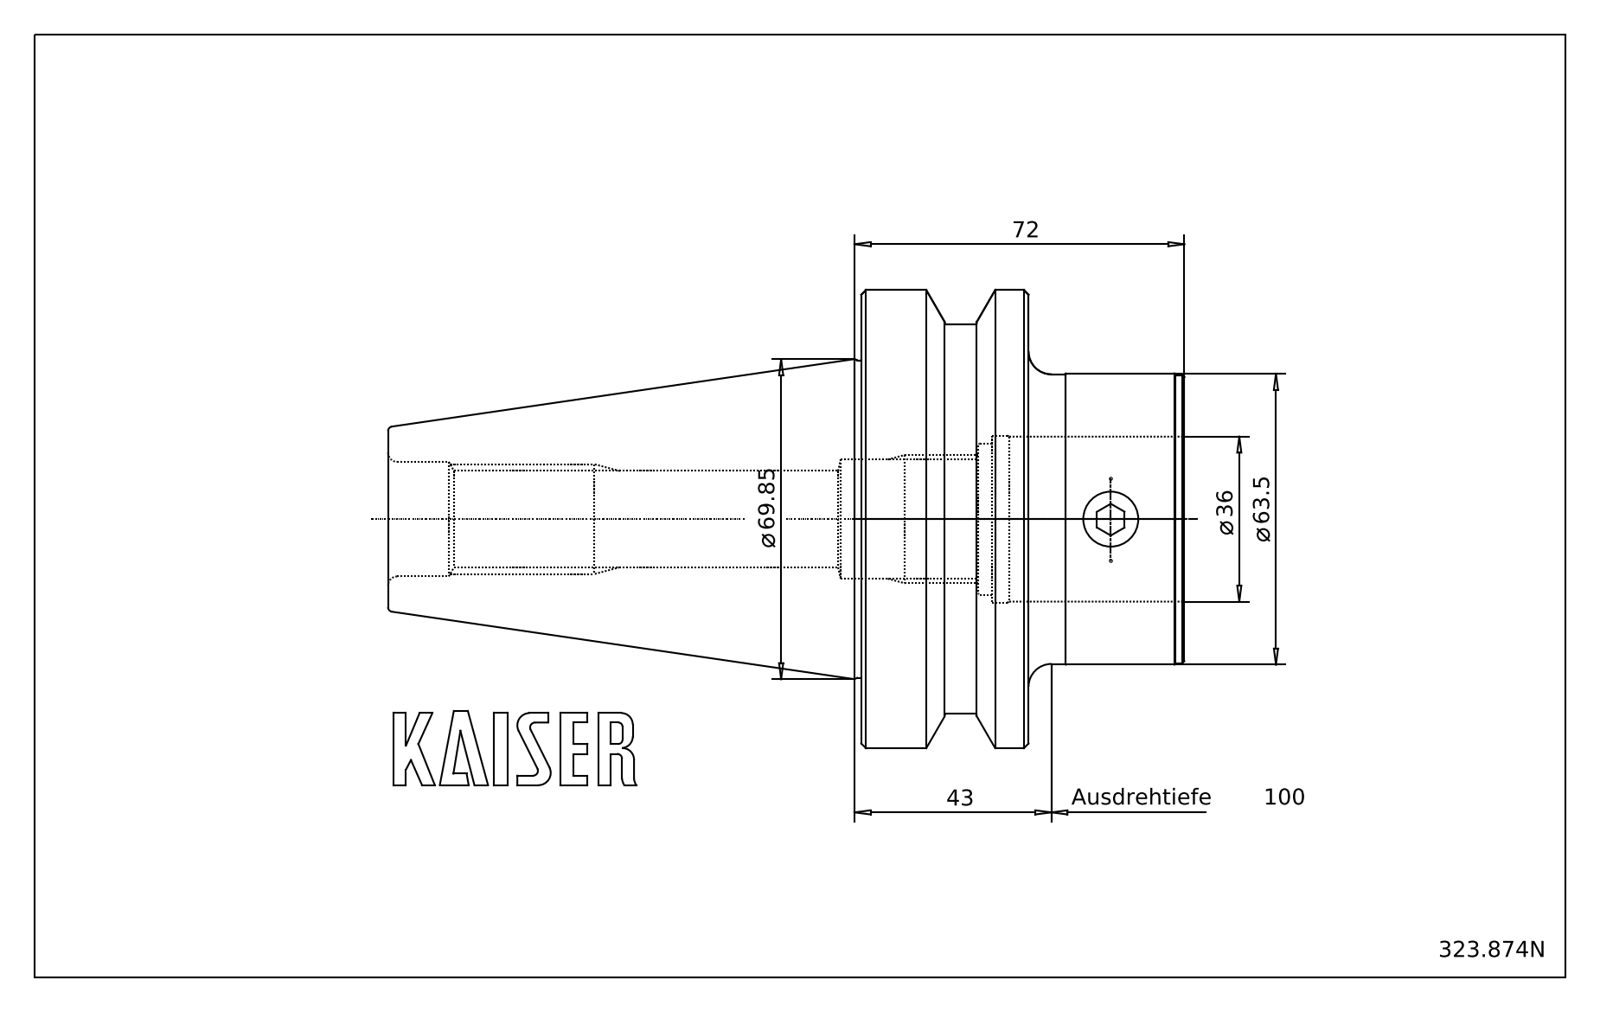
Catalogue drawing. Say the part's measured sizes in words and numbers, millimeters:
The part is named "323.874N Kaiser Schaft SK50B_BTxCKN6x100|690.436 Kaiser ETL M12 X 18 CK6;Schnitt-Linear austragen2; 323.874N Kaiser Schaft SK50B_BTxCKN6x100|323.874N Kaiser Schaft SK50B_BTxCKN6x100;Schnitt-Rotation4". Its 3-D file was written by "ACIS (automotive_design)". It is 4 solids with 257 faces: 90 planar, 69 cylindrical and 98 other. Overall it measures 173.8 by 100 by 100 millimeters. Its volume is 505 563 cubic millimeters and its surface area 68 915 square millimeters. Round holes: 3 of diameter 11.45, 3 of diameter 12.55, 3 of diameter 13.4, 1 of diameter 5, 1 of diameter 21.05, 1 of diameter 24, 1 of diameter 25, 1 of diameter 25.3, 1 of diameter 26.1, 1 of diameter 28, 1 of diameter 33, 1 of diameter 36. Round bosses or shafts: 3 of diameter 12, 1 of diameter 100, 1 of diameter 85, 1 of diameter 69.25, 1 of diameter 63.5, 1 of diameter 63.2. Partial cylindrical surfaces (rounded edges, fillets, slot ends): 2 of radius 5.5, 1 of radius 12.85. The main face-to-face distances are 36.5, 34, 70.5, 70.6, 173.8, 139.8, 103.3, 25.7, 30.7, 25.2. The hole center spacings are 11.15.
